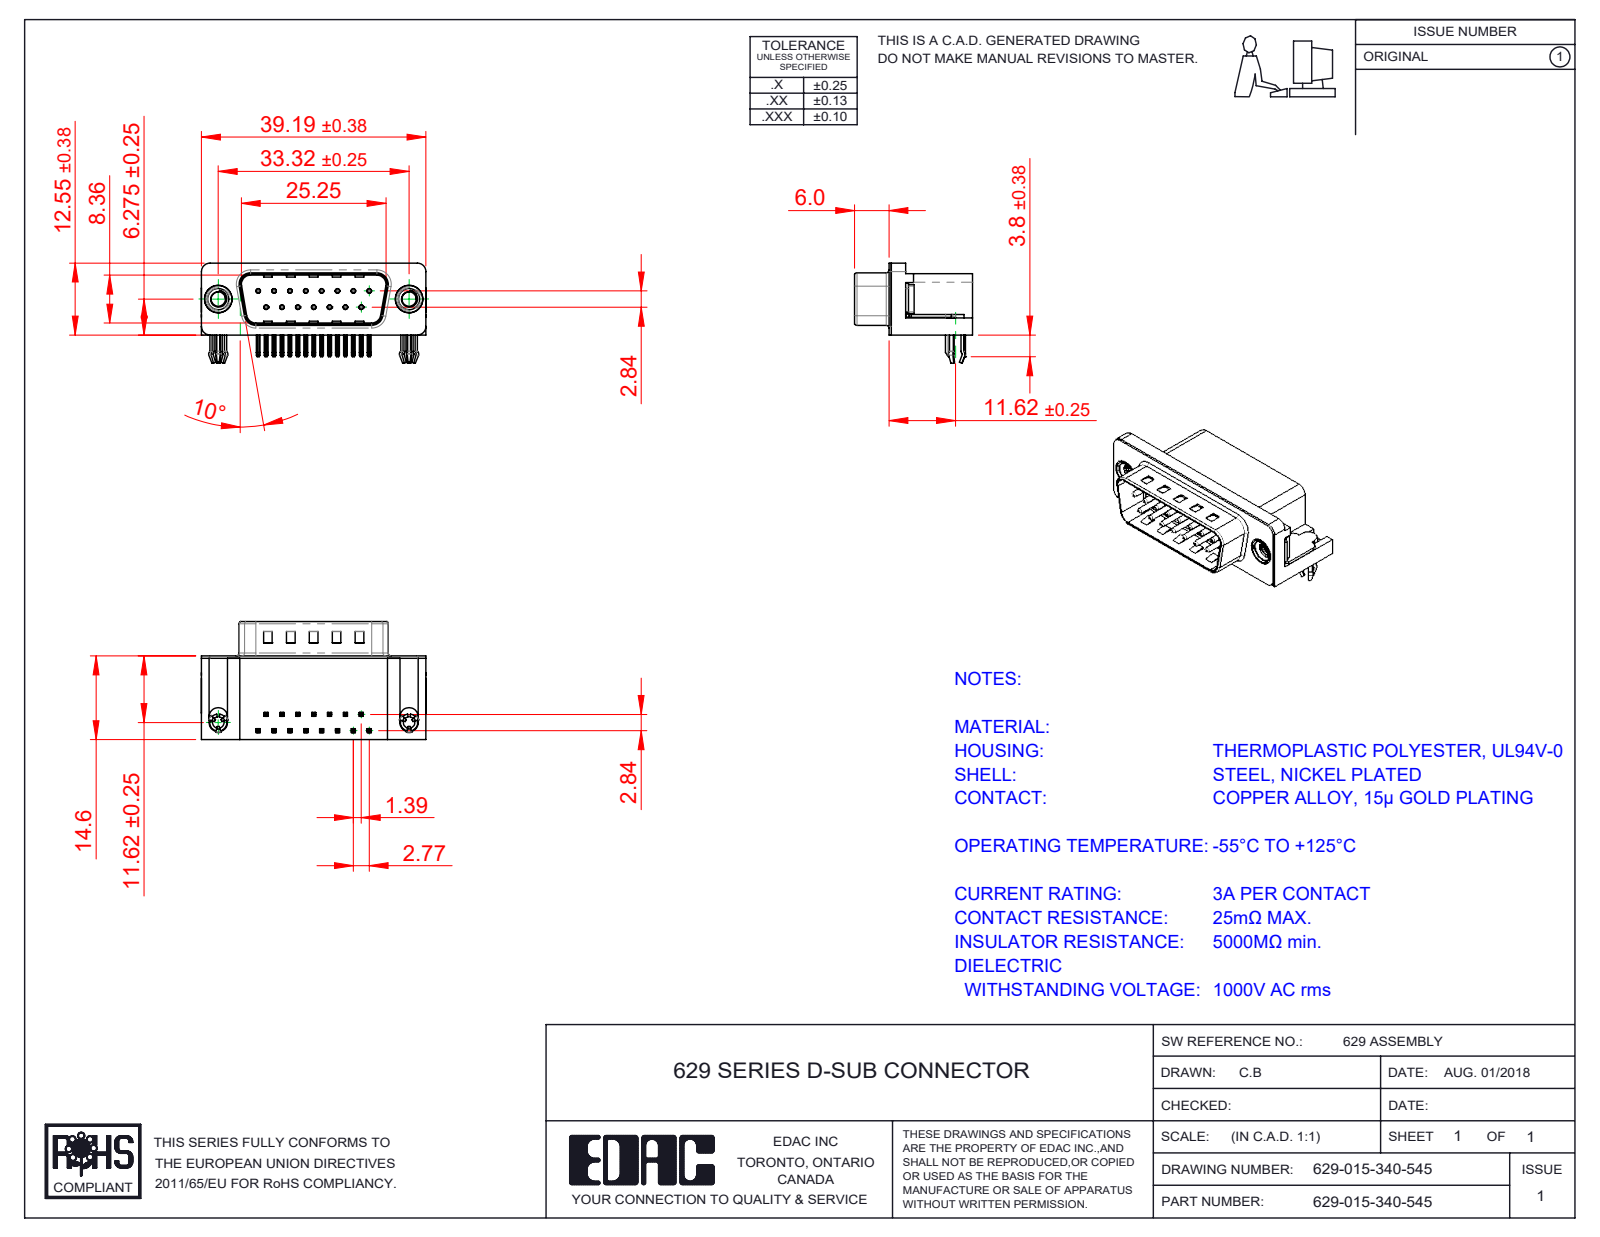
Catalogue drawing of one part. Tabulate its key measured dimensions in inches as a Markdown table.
| quantity | value |
| --- | --- |
| part name | 629 M3 Threaded Rivet; 629 Shell_15 Socket; 629 Housing_15 Socket; 629 Contact Top (+3 more) |
| STEP written by | SolidWorks 2020 (CONFIG_CONTROL_DESIGN) |
| units | inches |
| bodies | 21 solids, 1579 faces (929 planar, 455 cylindrical, 195 other) |
| overall size | 1.544 × 0.811 × 0.688 |
| volume | 0.31 in³ |
| surface area | 9.512 in² |
| round holes (diameter × count) | 0.014 × 15, 0.031 × 15, 0.079 × 2, 0.098 × 2, 0.157 × 2, 0.189 × 2, 0.197 × 2 |
| round bosses / shafts (diameter × count) | 0.03 × 15, 0.193 × 2, 0.187 × 2, 0.154 × 2, 0.118 × 2 |
| partial cylindrical surfaces (radius × count) | 0.01 × 72, 0.005 × 30, 0.039 × 16, 0.02 × 9, 0.063 × 8, 0.059 × 6, 0.035 × 4, 0.079 × 4 |
| main face-to-face distances | 0.016, 0.559, 0.407, 0.083, 0.575, 0.412, 0.067, 0.428, 0.345, 0.114 |
| hole center spacings | 0.124, 0.109, 0.218, 0.327, 0.436, 0.198, 0.198, 0.294 |
